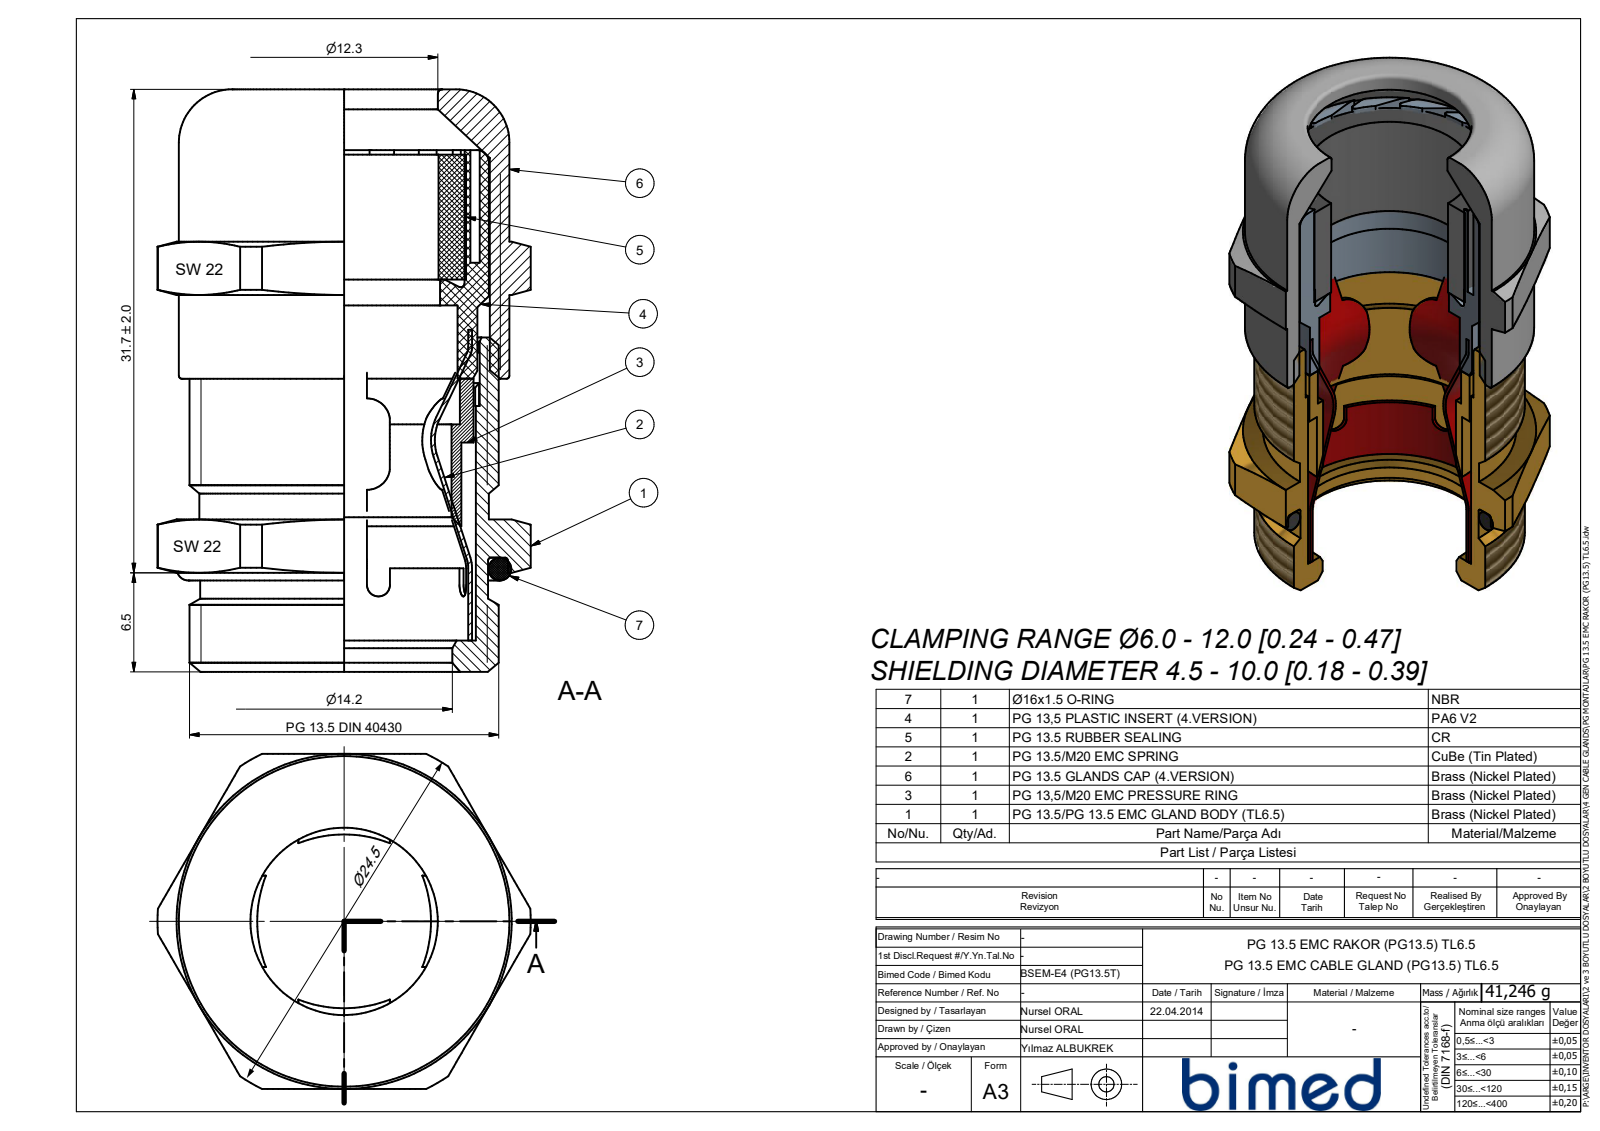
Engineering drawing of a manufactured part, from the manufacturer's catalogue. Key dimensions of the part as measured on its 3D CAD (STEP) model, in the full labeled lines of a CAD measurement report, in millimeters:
Part name (STEP PRODUCT): BSEM-E4-PG13T-WCL
STEP written by: SolidWorks 2021 (CONFIG_CONTROL_DESIGN)
Units: millimetres
Bodies: 1 solid, 92 faces (20 planar, 28 cylindrical, 44 other)
Overall size (bounding box): 38.2 × 24.5 × 22
Volume: 13 400 mm³ · Surface area: 3 566 mm²
Round bosses / shafts (diameter × count): ⌀21.7 ×1, ⌀20.3 ×1, ⌀19 ×1, ⌀18.9 ×1
Partial cylindrical surfaces — rounded edges, fillets, slot ends (radius × count): R12.2 ×1
Main face-to-face distances: 22, 38.3, 10, 28.2, 19.2, 9.2, 19, 3.5, 18.2, 24.7
